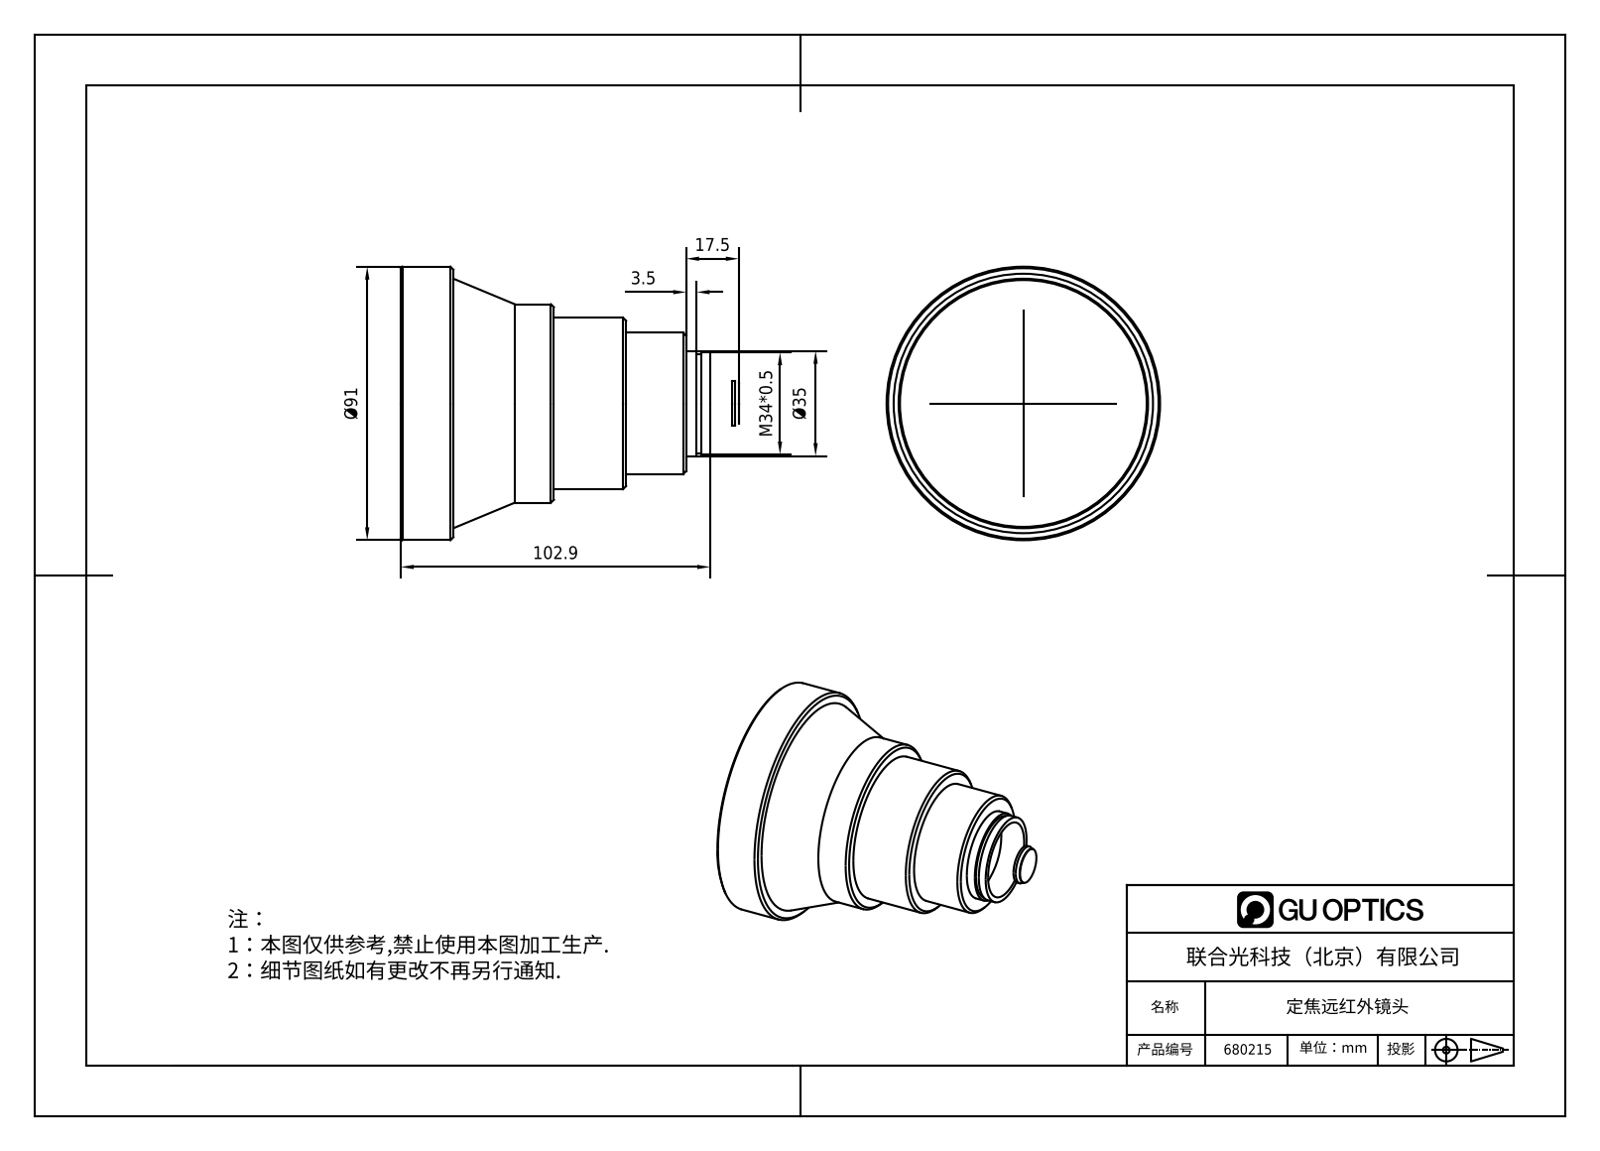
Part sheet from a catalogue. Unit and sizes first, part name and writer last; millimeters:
Units: millimetres
Overall size (bounding box): 112.64 × 91 × 91
Round holes (diameter × count): ⌀30 ×1, ⌀42.6 ×1, ⌀82.1 ×1, ⌀86.3 ×1
Round bosses / shafts (diameter × count): ⌀91 ×1, ⌀66 ×1, ⌀57 ×1, ⌀47 ×1, ⌀35 ×1, ⌀34 ×1, ⌀33 ×1, ⌀14.78 ×1
Main face-to-face distances: 75.45, 33.45, 42, 17.5, 94.95, 57.45, 24, 18, 77.45, 44
Volume: 273 044 mm³ · Surface area: 40 752 mm²
Bodies: 3 solids, 38 faces (15 planar, 13 cylindrical, 10 other)
Part name (STEP PRODUCT): LA-0004-3100F1.2消热差镜头外形图
STEP written by: SolidWorks 2020 (CONFIG_CONTROL_DESIGN)
